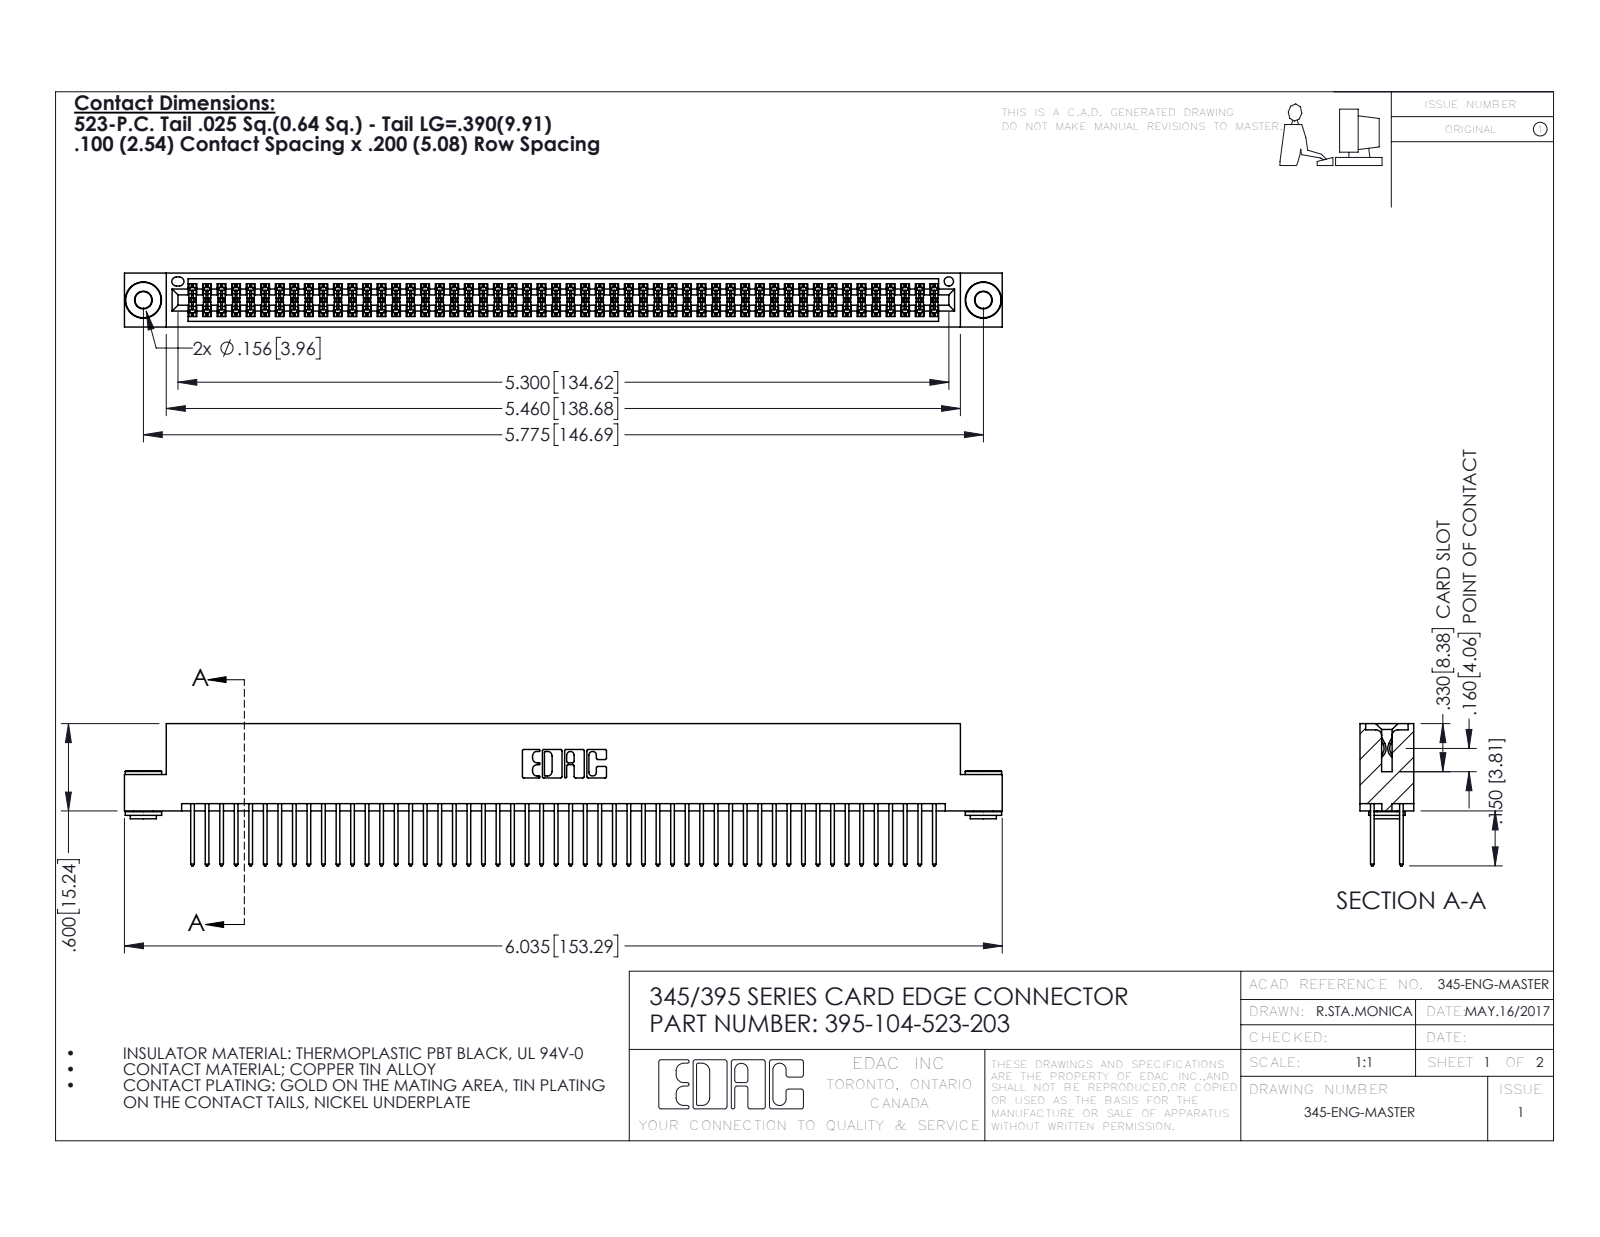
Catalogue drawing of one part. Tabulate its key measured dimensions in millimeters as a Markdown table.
| quantity | value |
| --- | --- |
| part name | 345-250-002_345-250-002-102; 345 Part_Flush Mounting Lugs - 0.156 Dia-TH; 395-104-523-203; 345-292-001_345-293-123 |
| STEP written by | SolidWorks 2016 (CONFIG_CONTROL_DESIGN) |
| units | millimeters |
| bodies | 107 solids, 5364 faces (3522 planar, 1834 cylindrical, 8 other) |
| overall size | 153.3 × 24.8 × 9.4 |
| volume | 15 200 mm³ |
| surface area | 23 850 mm² |
| round holes (diameter × count) | 2.9 × 2, 4 × 2, 1.6 × 1 |
| round bosses / shafts (diameter × count) | 6.4 × 2, 4.6 × 2, 3.5 × 2 |
| partial cylindrical surfaces (radius × count) | 0.2 × 156, 0.3 × 104, 0.3 × 22, 0.2 × 6, 0.8 × 6, 0.7 × 3, 0.4 × 2, 0.5 × 2 |
| main face-to-face distances | 1.8, 7.6, 5.1, 0.6, 2.5, 6.9, 9.4, 5.7, 4.4, 3.8 |
| hole center spacings | 6.9, 140.7, 146.7 |
